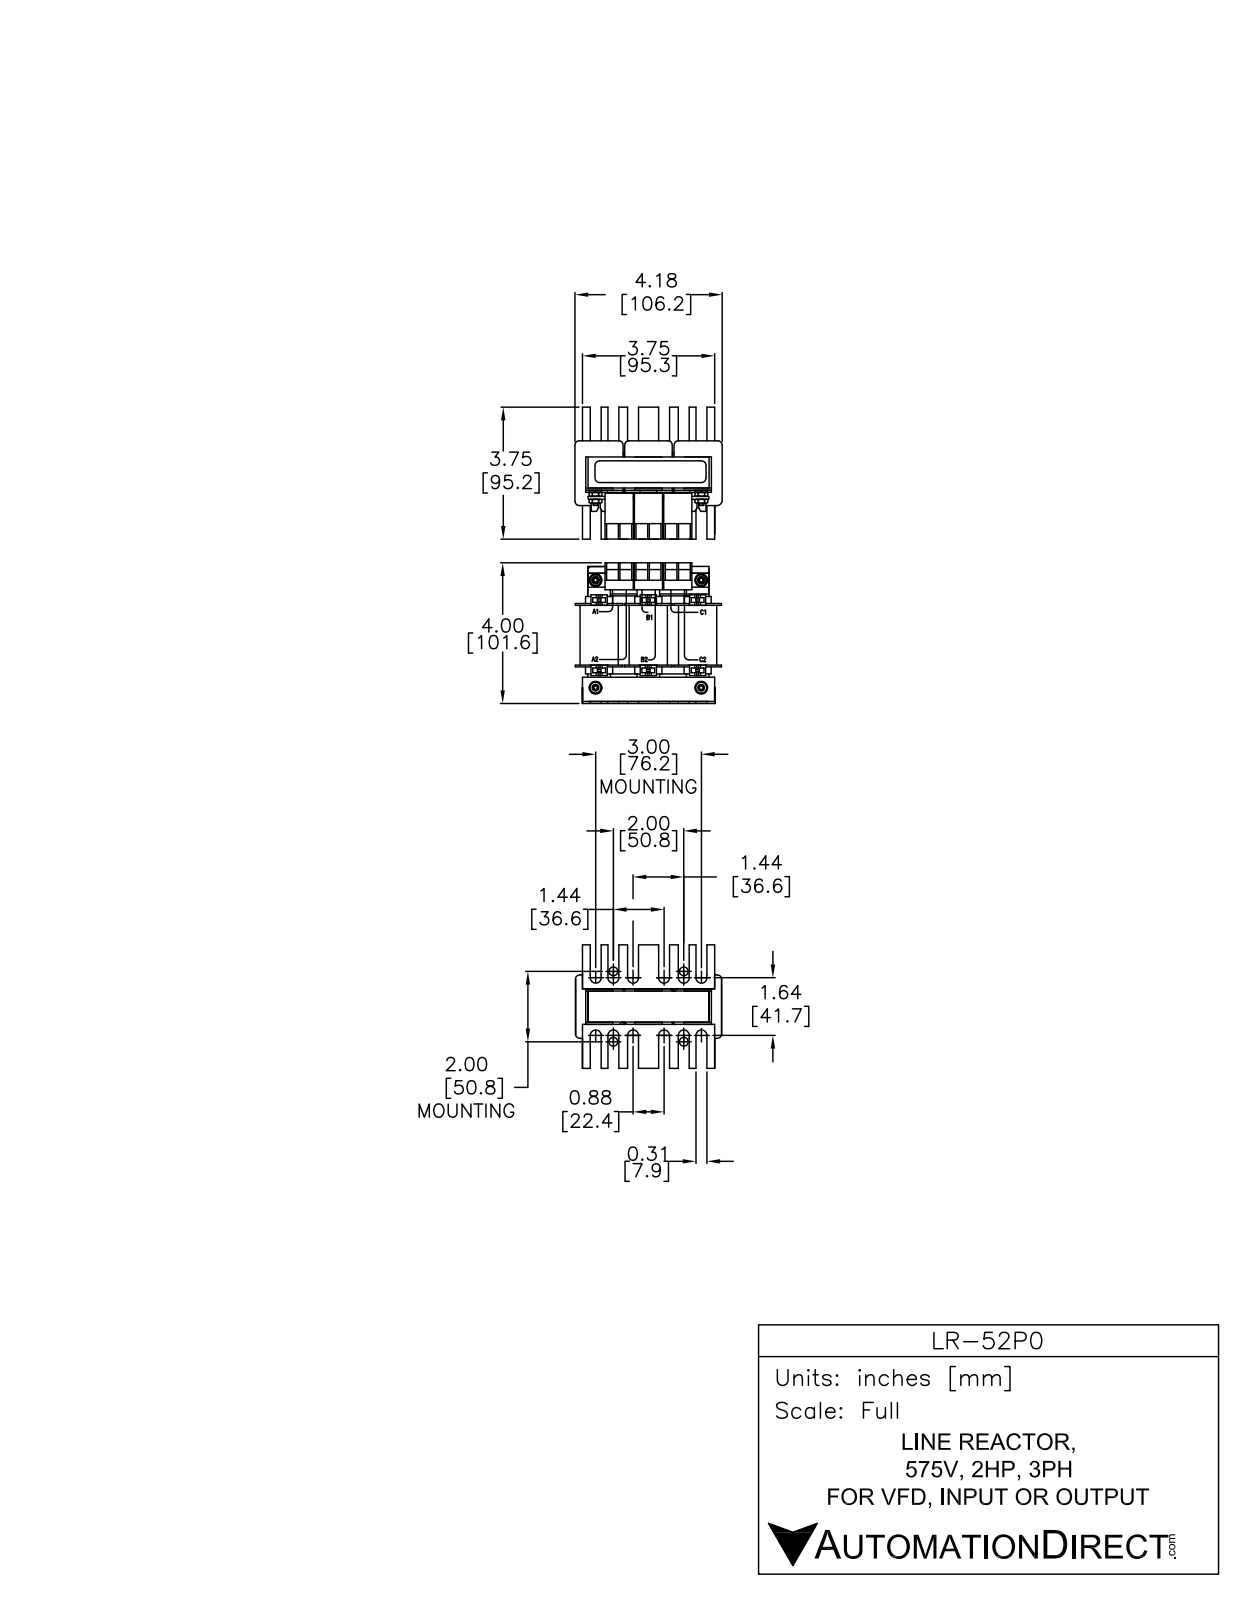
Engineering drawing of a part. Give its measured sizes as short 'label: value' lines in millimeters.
name: LR-52P0
written by: SolidWorks 2011 (AUTOMOTIVE_DESIGN)
unit: mm
bodies: 17 solids, 941 faces (743 planar, 198 cylindrical, 0 other)
size: 105.25 × 98.41 × 89.25
volume: 272 326 mm³; area: 99 223 mm²
bosses: 4× ⌀7.75, 4× ⌀3.5
rounds: 50× R4, 24× R1.82, 12× R8, 6× R3, 3× R0.86, 2× R1.25
face distances: 5, 21.5, 2.75, 51, 26.25, 26.5, 7.5, 29, 71, 2.5
